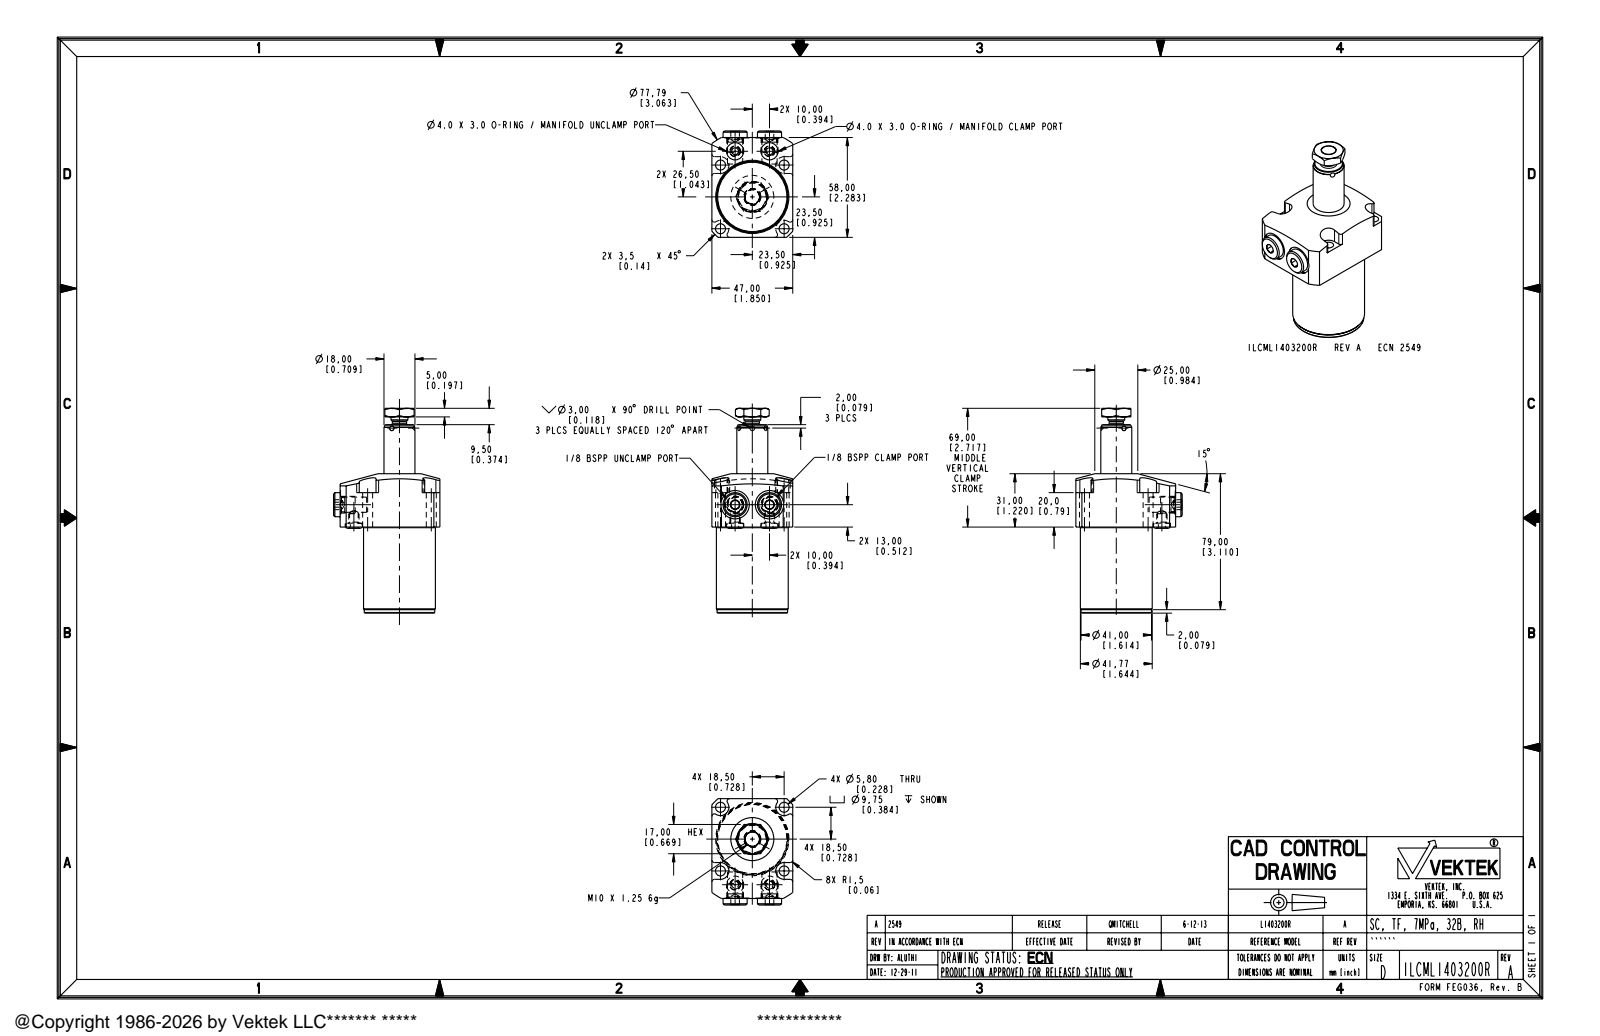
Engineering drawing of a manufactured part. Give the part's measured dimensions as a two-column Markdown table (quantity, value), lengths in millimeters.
| quantity | value |
| --- | --- |
| part name | ILCML1403200L |
| STEP written by | PRO/ENGINEER BY PARAMETRIC TECHNOLOGY CORPORATION, 2007460 (AUTOMOTIVE_DESIGN_CC2) |
| units | millimeters |
| bodies | 3 solids, 215 faces (68 planar, 70 cylindrical, 77 other) |
| overall size | 119 × 61.81 × 47 |
| volume | 148 841 mm³ |
| surface area | 24 392 mm² |
| round holes (diameter × count) | 5 × 4, 5.8 × 4, 8.84 × 2, 10 × 2, 16.5 × 2, 8.75 × 1 |
| round bosses / shafts (diameter × count) | 8.25 × 3, 14 × 2, 9.73 × 2, 6 × 2, 41.77 × 1, 41 × 1, 18 × 1, 9.87 × 1 |
| partial cylindrical surfaces (radius × count) | 1.5 × 8, 4.88 × 4, 38.9 × 1 |
| main face-to-face distances | 47, 50, 58, 31, 11, 20, 5, 81, 70, 119 |
| hole center spacings | 26.16, 37, 11.67, 20, 28.32, 29.6, 45.8, 52.33 |
